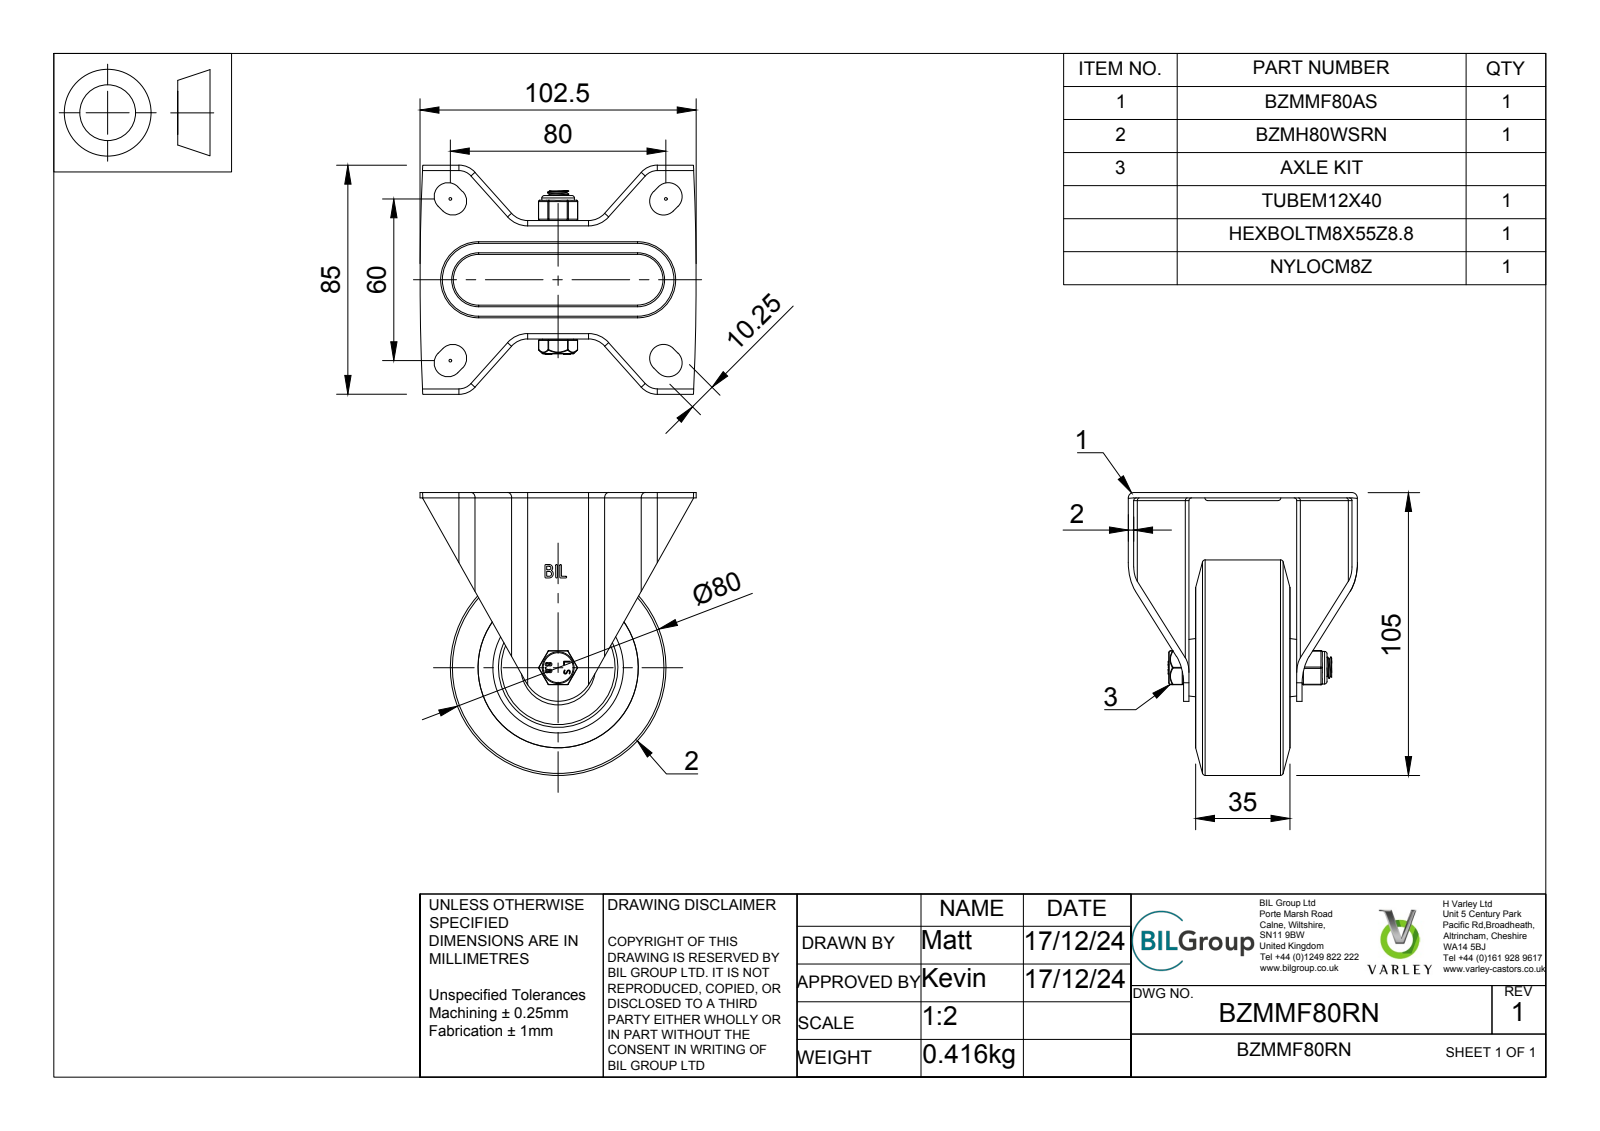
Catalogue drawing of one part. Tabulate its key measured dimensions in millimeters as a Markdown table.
| quantity | value |
| --- | --- |
| part name | BZMMF80RN v3; BZMMF80AS - 40 v2; ZINC PLATED, PRESSED STEEL BRACKET; BZMH80WSRN v1 (+8 more) |
| STEP written by | Autodesk Translation Framework v13.20.0.188 (AP242_MANAGED_MODEL_BASED_3D_ENGINEERING_MIM_LF) |
| units | millimeters |
| bodies | 7 solids, 389 faces (125 planar, 161 cylindrical, 103 other) |
| overall size | 105 × 102.5 × 85 |
| volume | 172 498 mm³ |
| surface area | 77 471 mm² |
| round holes (diameter × count) | 0.66 × 2, 8 × 1, 8.25 × 1, 8.4 × 1, 8.6 × 1, 12.2 × 1, 59.5 × 1 |
| round bosses / shafts (diameter × count) | 80 × 1, 12.1 × 1, 11.9 × 1, 11.5 × 1, 7.87 × 1, 6.45 × 1 |
| partial cylindrical surfaces (radius × count) | 0.5 × 18, 0.25 × 12, 1 × 12, 2 × 8, 4 × 8, 5.12 × 8, 8 × 8, 0.33 × 4 |
| main face-to-face distances | 2, 5.16, 42, 40, 3.16, 7.16, 4.5, 39.5, 2.5, 37.5 |
| hole center spacings | 3.22, 2.49 |
